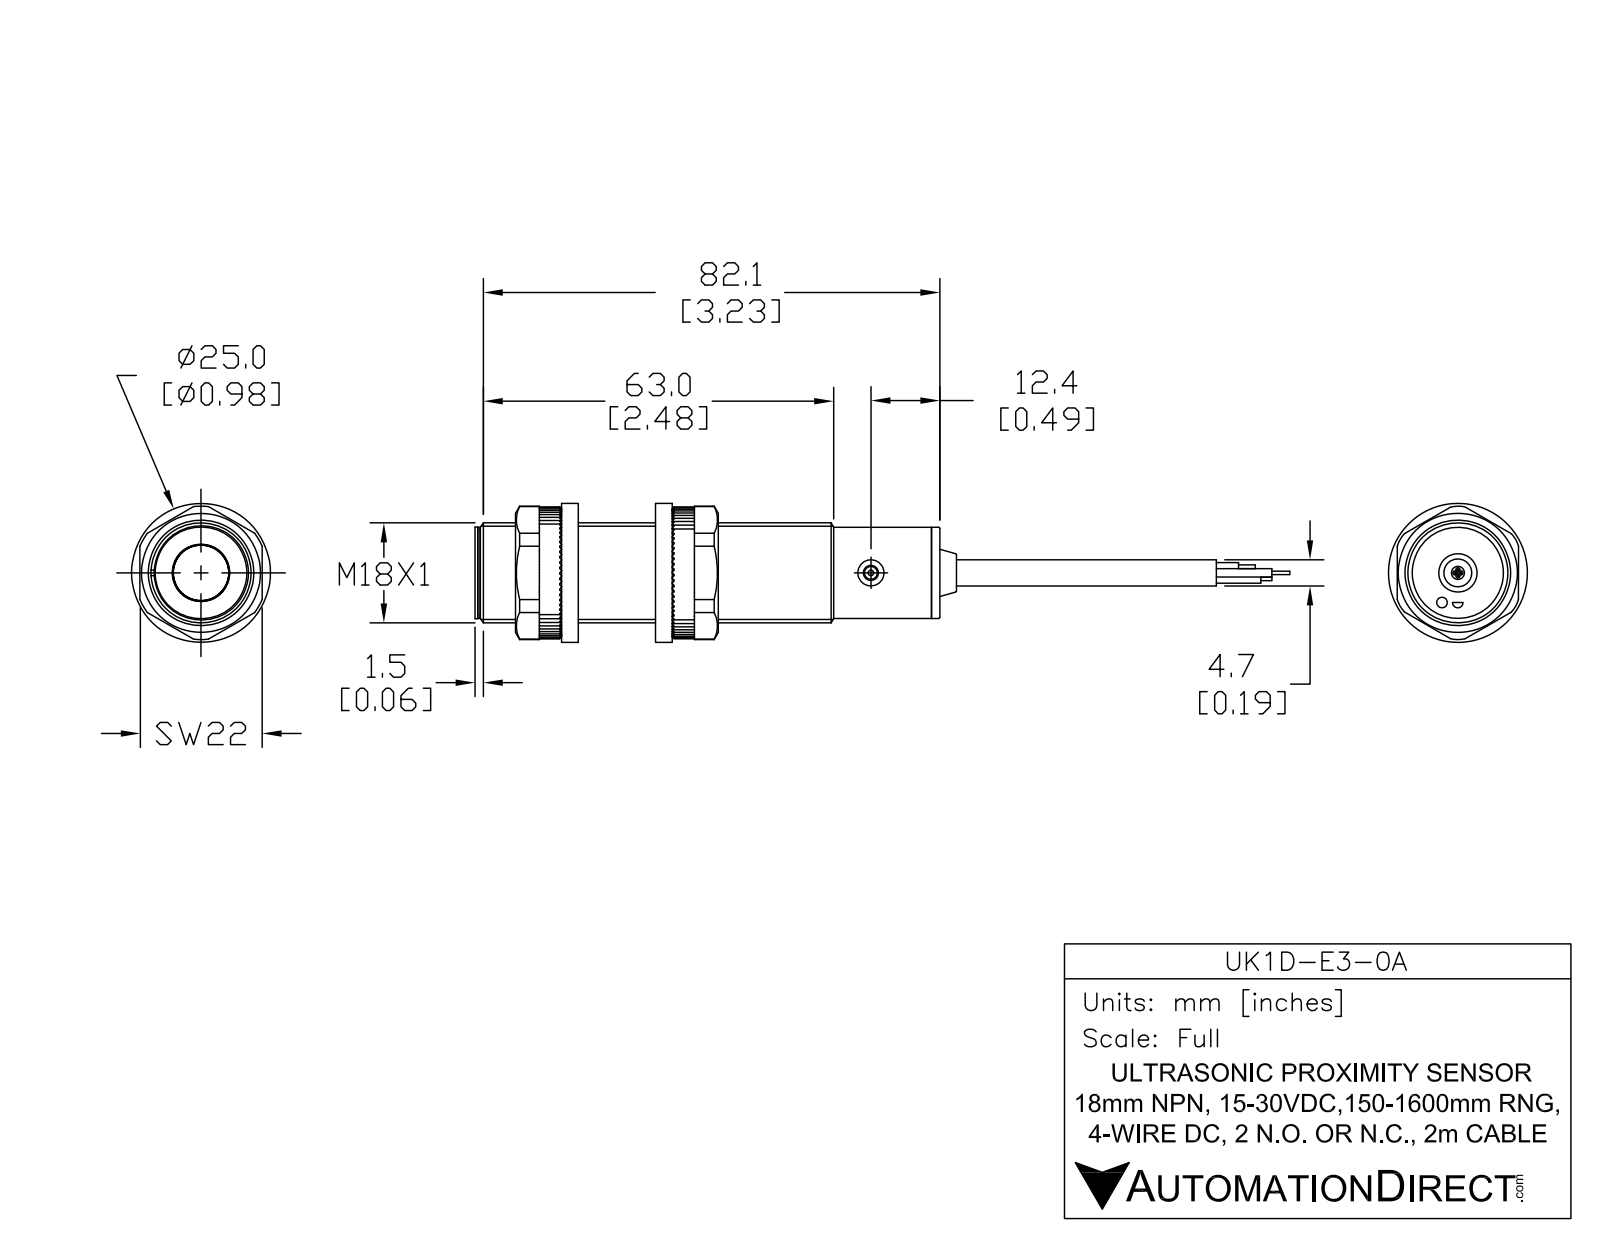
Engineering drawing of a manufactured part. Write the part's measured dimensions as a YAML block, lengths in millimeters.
part_name: "UK1D-E3-0A"
step_written_by: "SolidWorks 2017 (AUTOMOTIVE_DESIGN)"
units: millimeters
bodies: {solids: 6, faces: 55, planar: 17, cylindrical: 24, other: 14}
overall_size: [122.7, 18, 18]
volume: 21060
surface_area: 6897
round_holes:
  - {diameter: 4.7, count: 2}
  - {diameter: 2.7, count: 1}
round_bosses_or_shafts:
  - {diameter: 18, count: 1}
  - {diameter: 16.4, count: 1}
  - {diameter: 15.8, count: 1}
  - {diameter: 9.5, count: 1}
  - {diameter: 4.8, count: 1}
  - {diameter: 2.3, count: 1}
face_to_face_distances: [81.1, 82.6, 1.5, 1, 82.1, 83.6, 1, 82.1, 83.6, 82.7]
